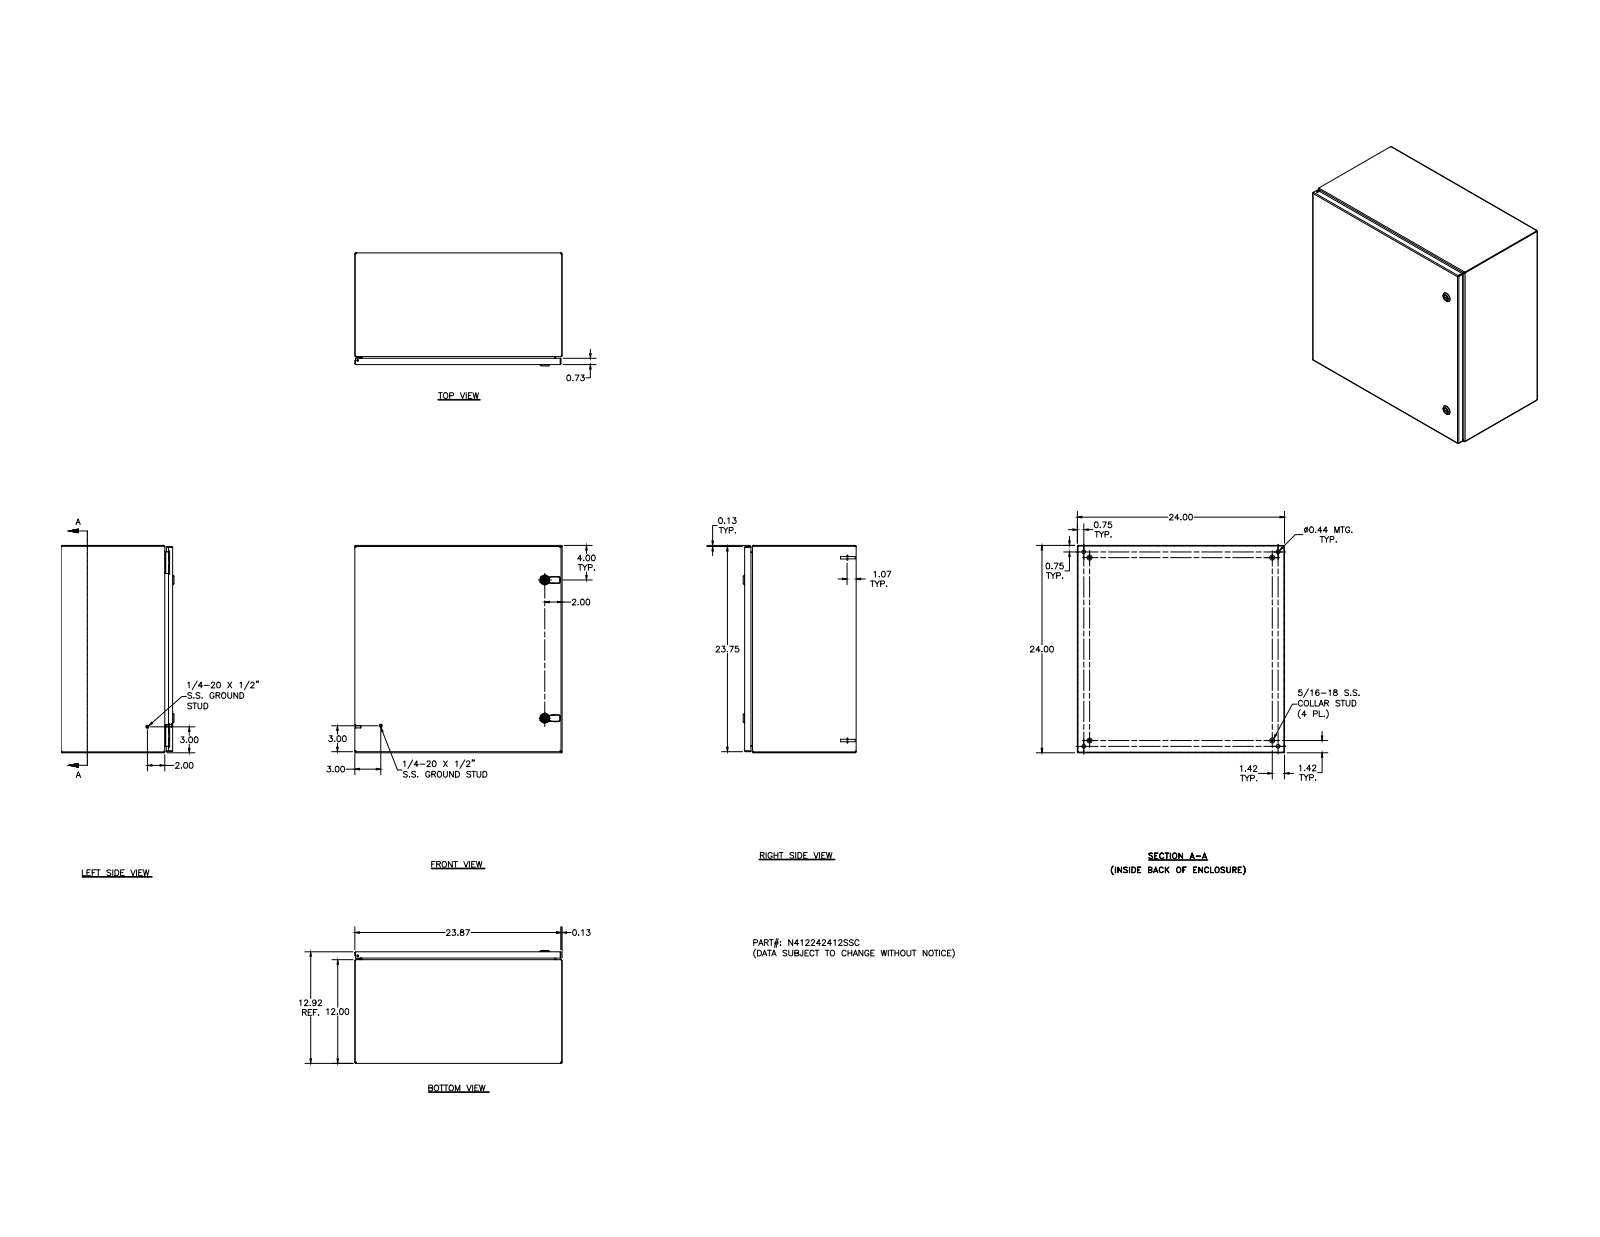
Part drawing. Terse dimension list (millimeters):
name: N412242412SSC; N412242412SSCBKP; 388151; N4122424SSCLID (+8 more)
written by: Autodesk Inventor 2011 (AUTOMOTIVE_DESIGN)
unit: mm
bodies: 42 solids, 1682 faces (706 planar, 600 cylindrical, 376 other)
size: 609.6 × 609.6 × 332.1
volume: 3 037 000 mm³; area: 3 243 000 mm²
holes: 5× ⌀4.8, 4× ⌀2.4, 4× ⌀3.9, 4× ⌀4.2, 4× ⌀4.4, 4× ⌀11.1, 2× ⌀4, 2× ⌀5, 2× ⌀8, 2× ⌀10, 2× ⌀10.2, 2× ⌀16.1
bosses: 10× ⌀6.4, 4× ⌀14.3, 4× ⌀9.1, 4× ⌀8.1, 4× ⌀7.6, 4× ⌀7, 4× ⌀6.5, 4× ⌀4.2
rounds: 30× R0.8, 26× R1.3, 20× R2.7, 18× R0.4, 15× R0.5, 14× R3.2, 8× R0.8, 8× R1.8
face distances: 1.9, 607.7, 326.2, 609.6, 605.8, 328.1, 324.3, 302.9, 23.3, 18.8
hole spacings: 508, 0.4, 16.8, 571.5, 580.9, 0.5, 12.7, 16.5
